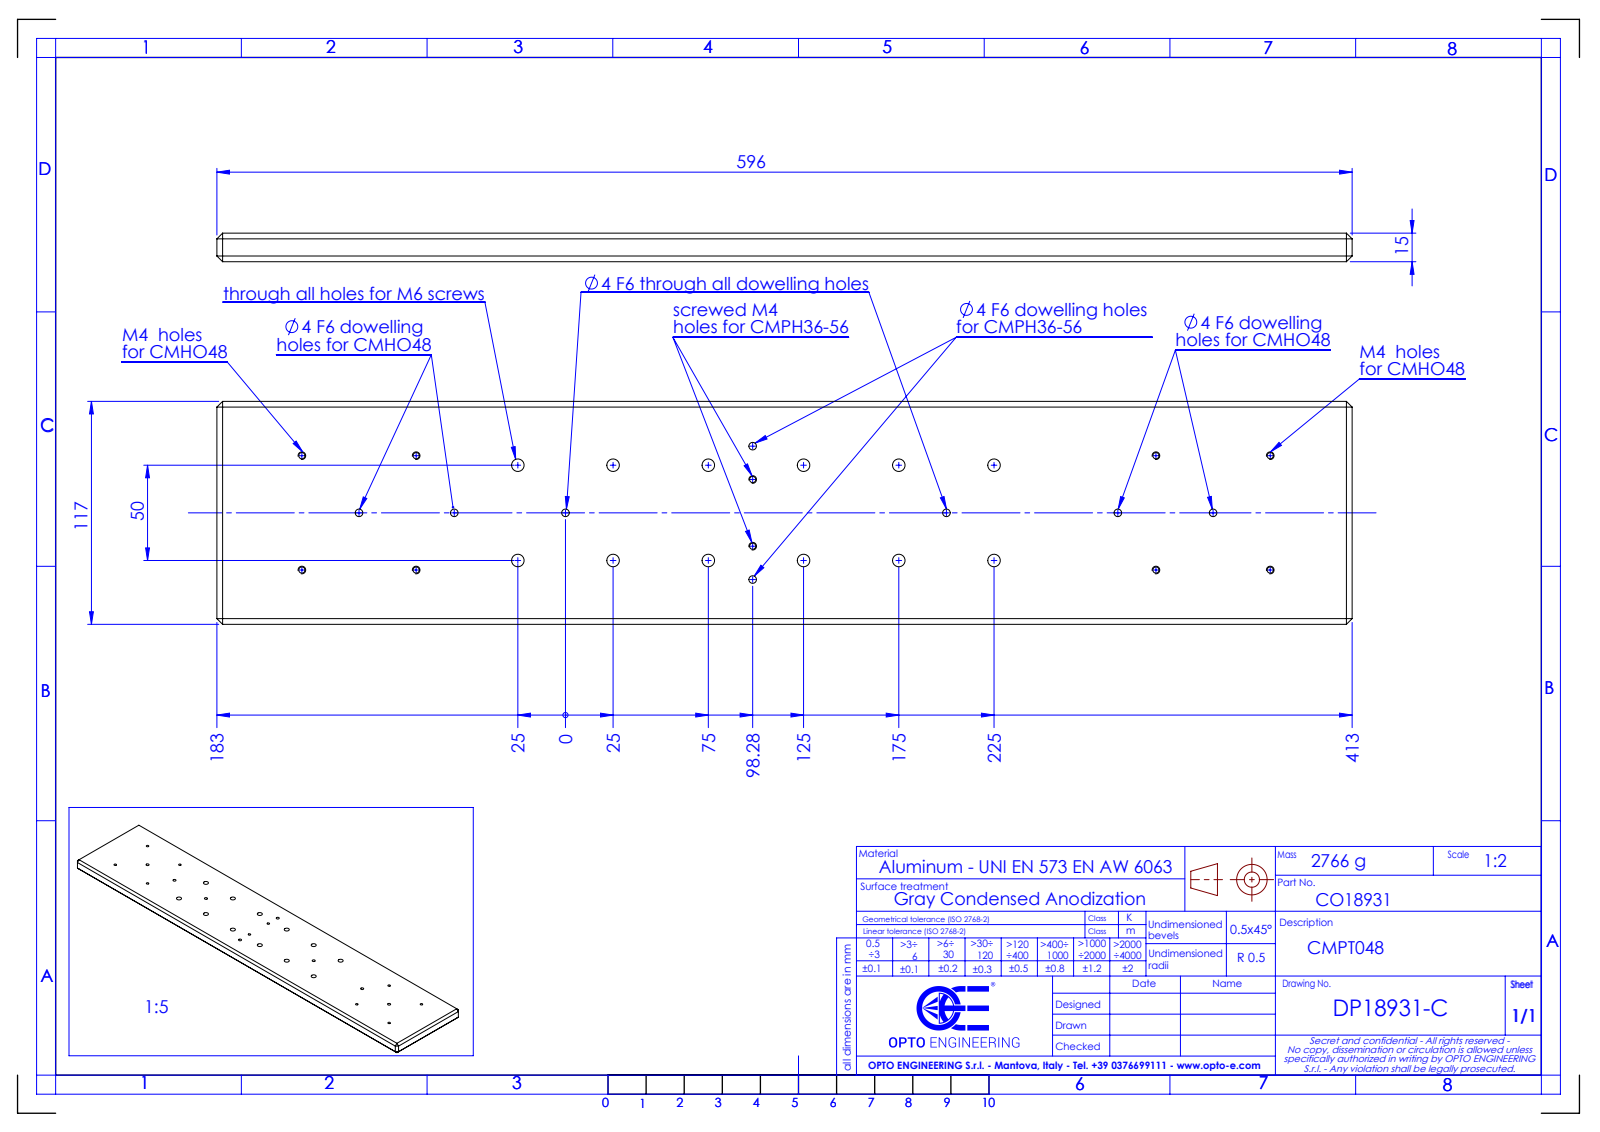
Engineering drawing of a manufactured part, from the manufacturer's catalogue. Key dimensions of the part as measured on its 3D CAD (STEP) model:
Part name (STEP PRODUCT): DP18931-C_CMPT048
STEP written by: SolidWorks 2021 (AUTOMOTIVE_DESIGN)
Units: millimetres
Bodies: 1 solid, 92 faces (32 planar, 60 cylindrical, 0 other)
Overall size (bounding box): 596 × 117 × 15
Volume: 1 025 000 mm³ · Surface area: 160 960 mm²
Round holes (diameter × count): ⌀6.6 ×12, ⌀3.3 ×10, ⌀4 ×8
Main face-to-face distances: 15, 117, 89.08, 596, 427.74, 427.73, 5, 499.85, 10, 413.13
Hole centre spacings: 50, 70.71, 35.36, 42.43, 60, 100, 111.8, 150
